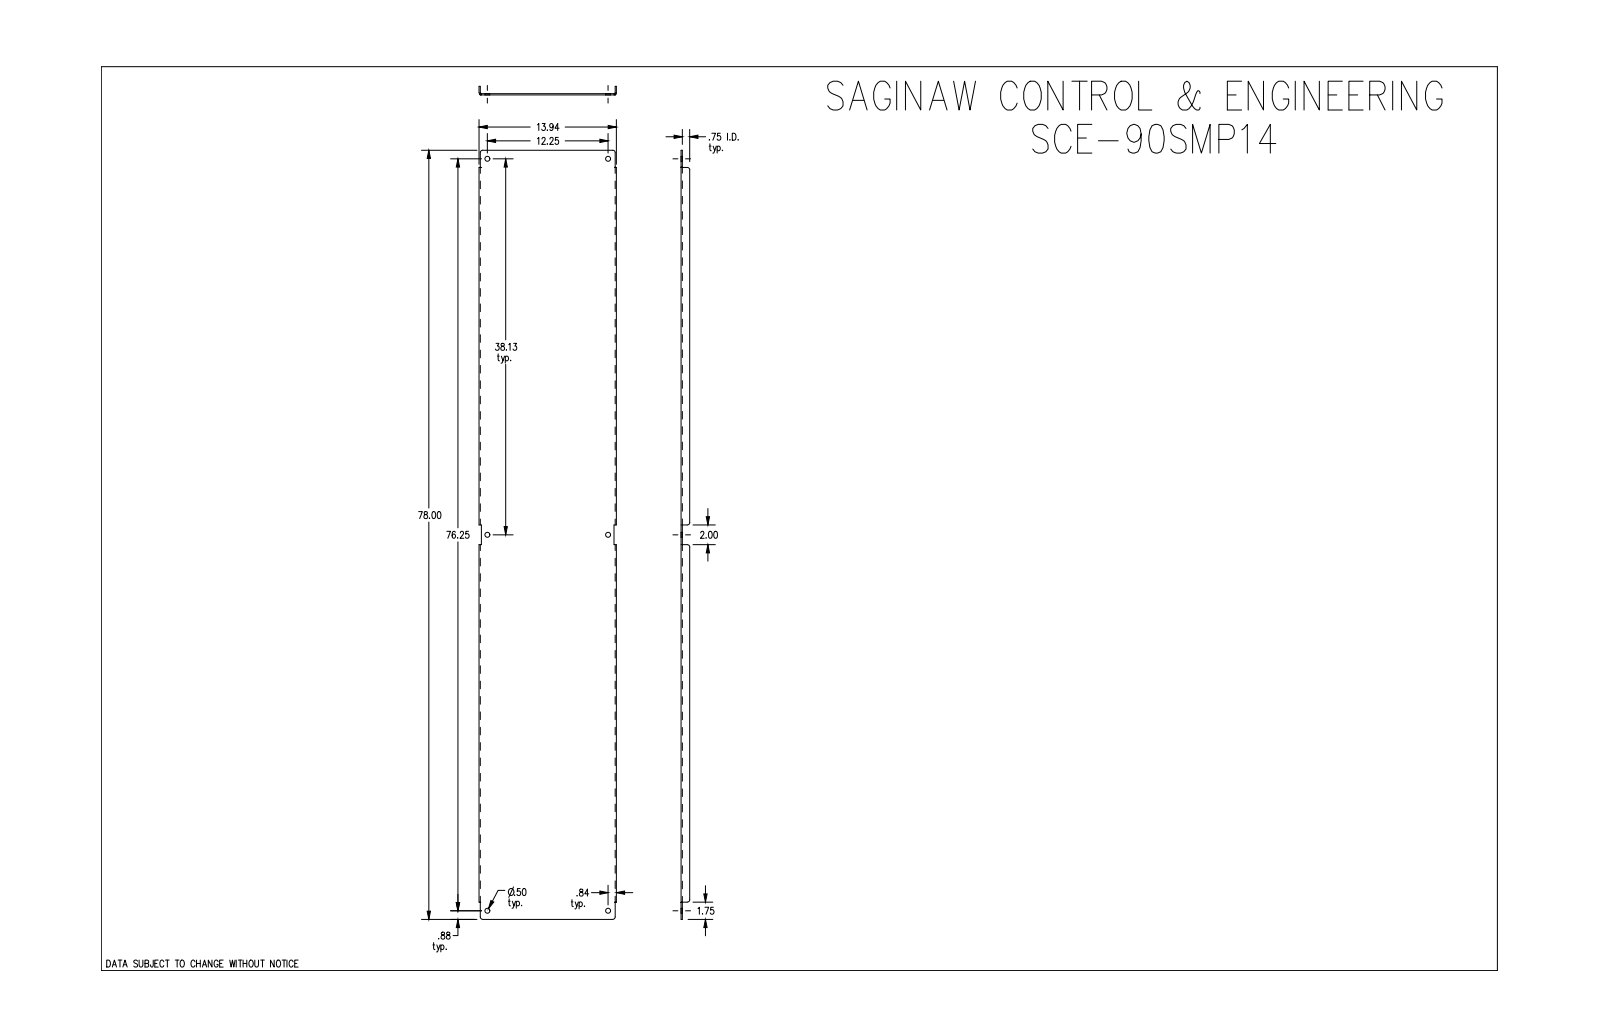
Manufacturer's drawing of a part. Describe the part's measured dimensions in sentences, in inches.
The part is named "SCE-90SMP14". Its 3-D file was written by "SolidWorks 2019 (CONFIG_CONTROL_DESIGN)". It is 1 solid with 68 faces: 30 planar, 26 cylindrical and 12 other. Overall it measures 78 by 13.938 by 0.875 inches. Its volume is 147.7 cubic inches and its surface area 2 389 square inches. Round holes: 6 of diameter 0.5. Partial cylindrical surfaces (rounded edges, fillets, slot ends): 8 of radius 0.25, 2 of radius 0.112, 2 of radius 0.237. The main face-to-face distances are 0.125, 0.125, 13.813, 13.687, 13.938, 0.75, 0.875, 78, 0.237, 13.701. The hole center spacings are 38.125, 40.045, 12.25, 76.25, 77.228.
